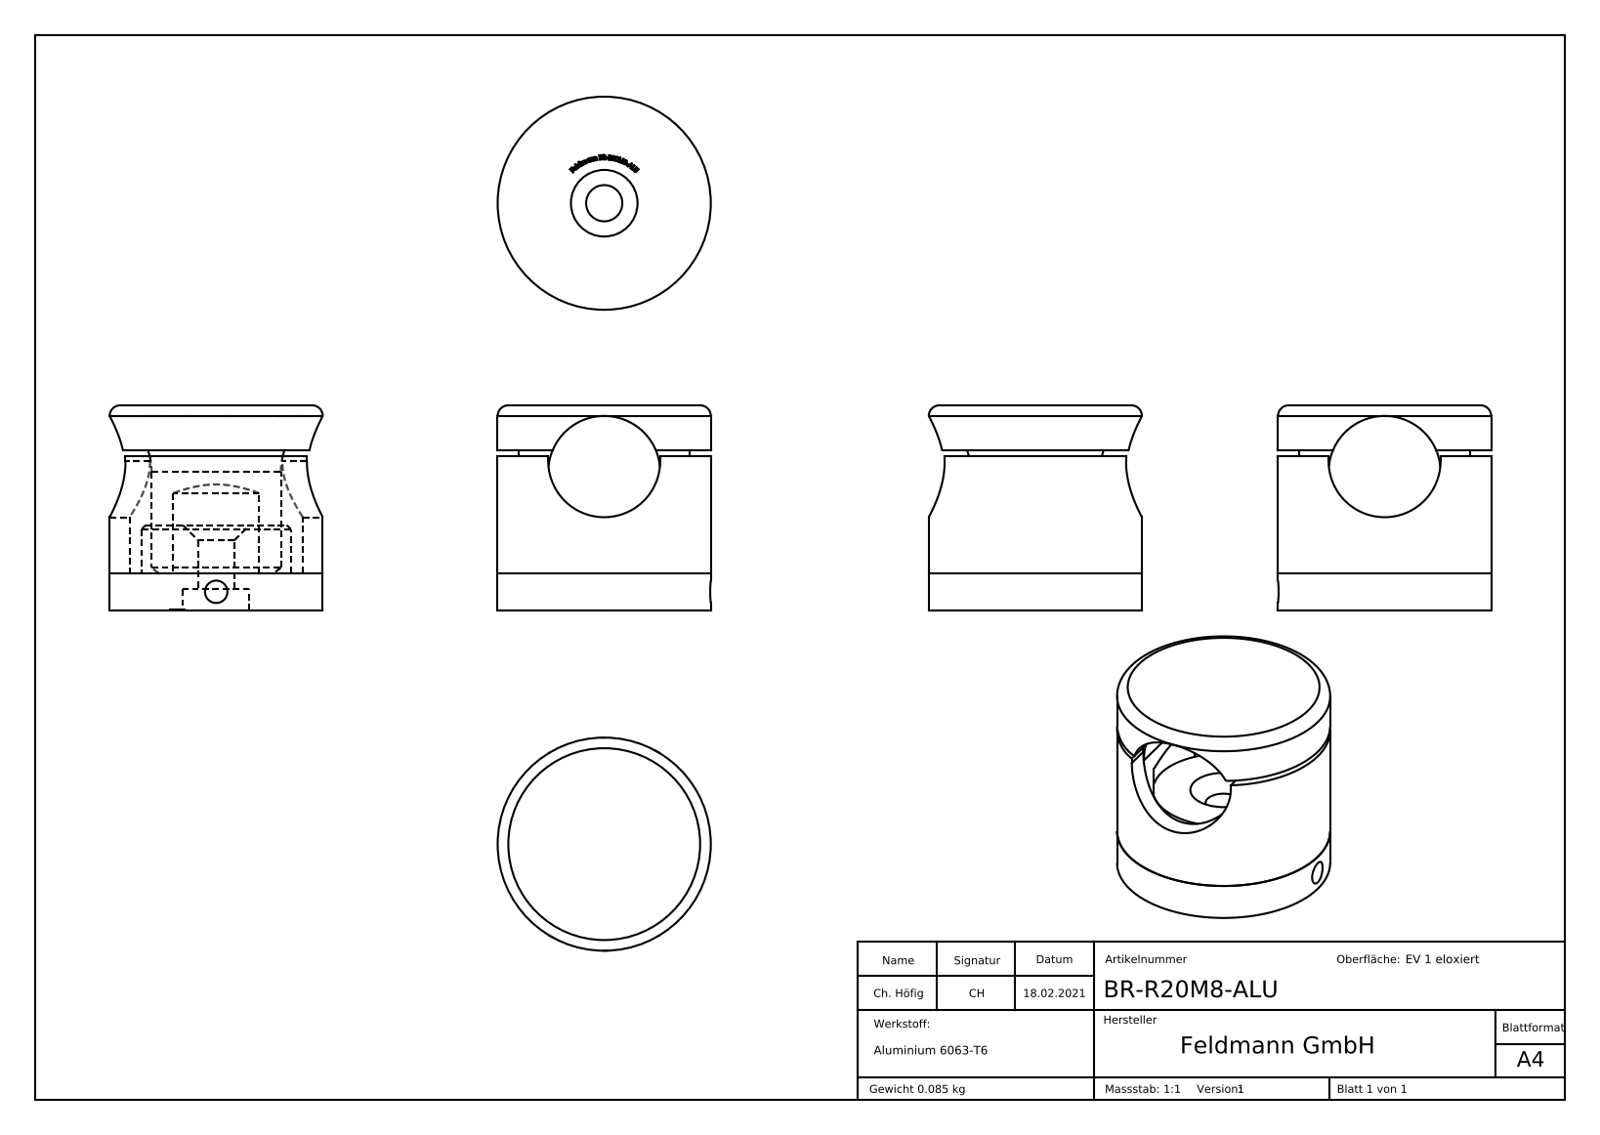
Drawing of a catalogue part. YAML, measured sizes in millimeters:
part_name: "BR-R20M8-ALU; BR-R1XM8-XXX Teil2; BR-R1XM8-XXX Teil1; BR-R1XM8-XXX Teil1_BR-2XM8-ALU Teil1 (+3 more)"
step_written_by: "SolidWorks 2018 (CONFIG_CONTROL_DESIGN)"
units: millimeters
bodies: {solids: 3, faces: 324, planar: 185, cylindrical: 23, other: 116}
overall_size: [40, 40, 38.5]
volume: 31486
surface_area: 15505
round_holes:
  - {diameter: 4.2, count: 1}
  - {diameter: 6.8, count: 1}
  - {diameter: 12.5, count: 1}
  - {diameter: 32.5, count: 1}
round_bosses_or_shafts:
  - {diameter: 40, count: 1}
  - {diameter: 28, count: 1}
partial_cylinders:
  - {radius: 10.5, count: 2}
  - {radius: 13.25, count: 1}
  - {radius: 16.05, count: 1}
face_to_face_distances: [7, 38.5, 31.5, 16, 9, 22.5, 30, 23, 14, 8.5]
